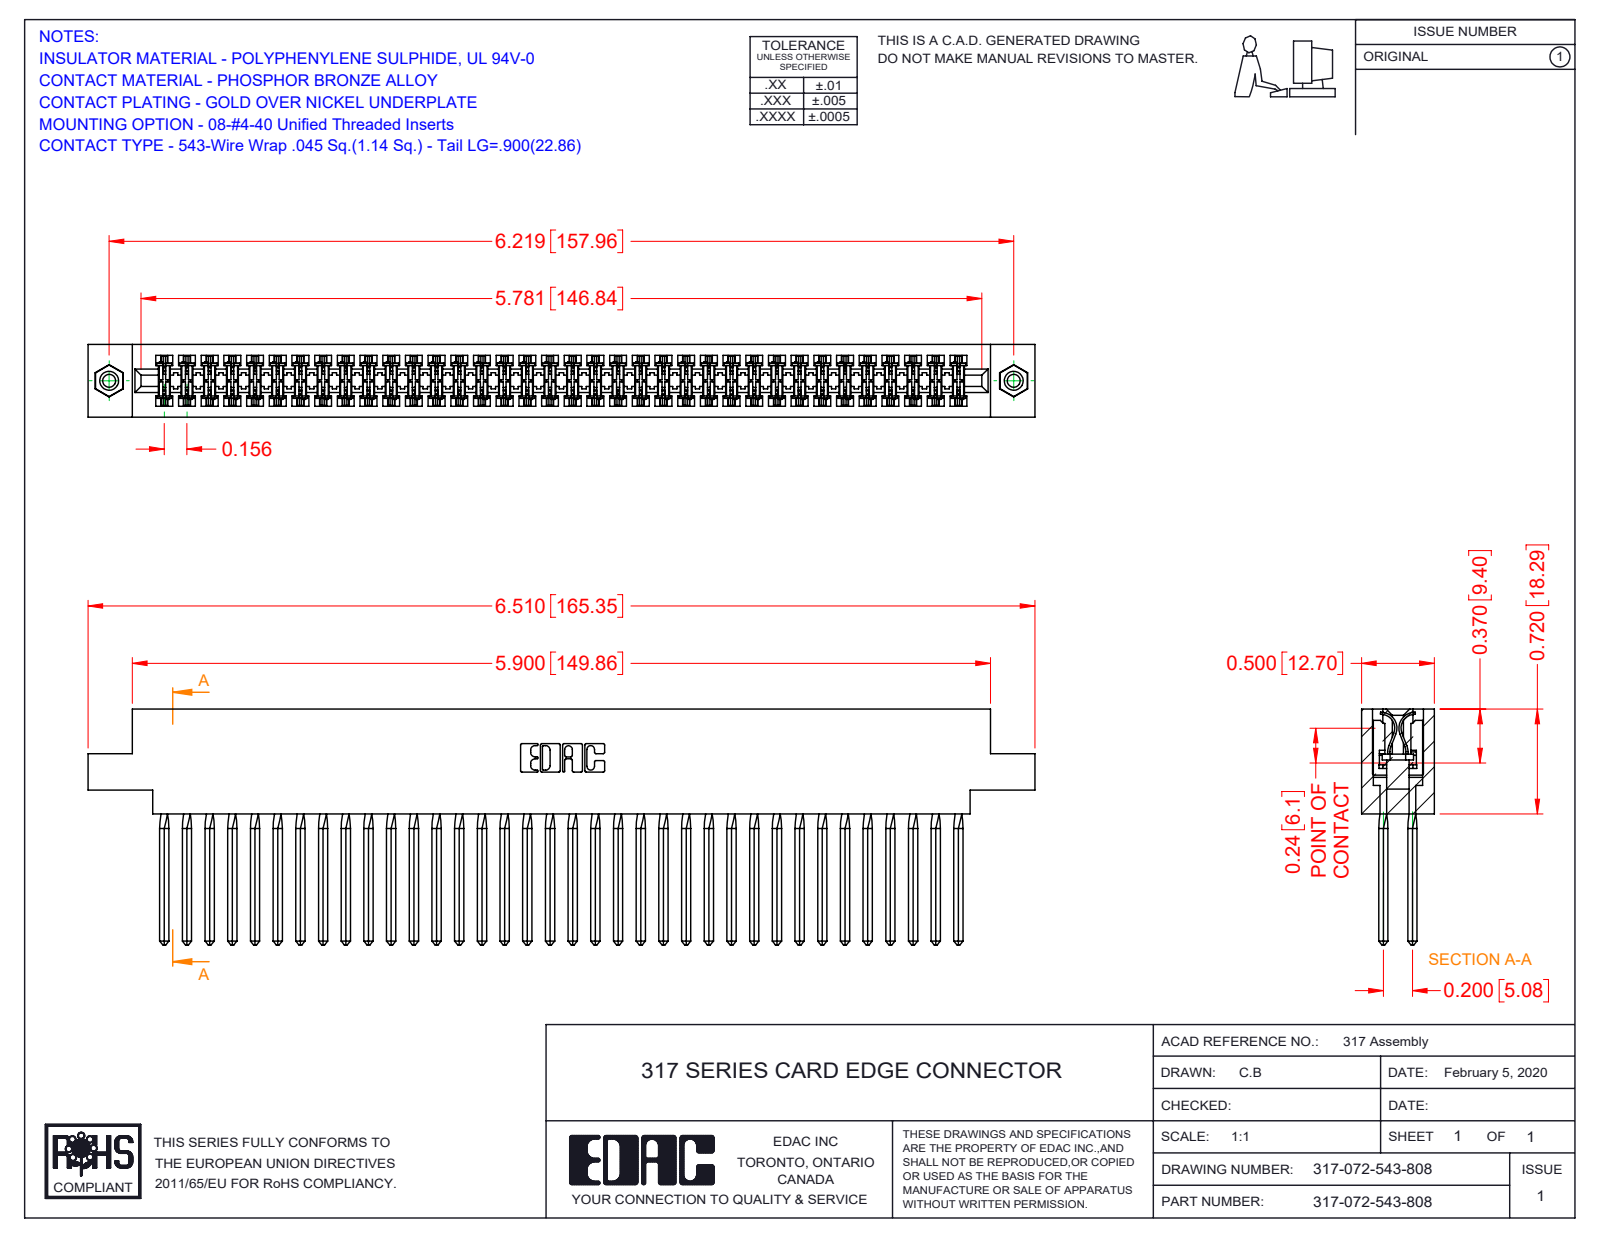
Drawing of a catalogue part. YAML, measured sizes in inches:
part_name: "317-290-001_543; 317-072-543-808; 345-250-001_345-250-003-102; 317 Part_.156 Dia - TI"
step_written_by: "SolidWorks 2016 (CONFIG_CONTROL_DESIGN)"
units: inches
bodies: {solids: 75, faces: 6570, planar: 5346, cylindrical: 920, other: 304}
overall_size: [6.51, 1.62, 0.5]
volume: 1.703
surface_area: 65.27
round_holes:
  - {diameter: 0.089, count: 2}
  - {diameter: 0.125, count: 2}
  - {diameter: 0.156, count: 2}
round_bosses_or_shafts:
  - {diameter: 0.155, count: 2}
partial_cylinders:
  - {radius: 0.015, count: 144}
  - {radius: 0.01, count: 22}
  - {radius: 0.007, count: 6}
  - {radius: 0.031, count: 6}
  - {radius: 0.026, count: 3}
  - {radius: 0.095, count: 2}
  - {radius: 0.1, count: 2}
  - {radius: 0.11, count: 2}
face_to_face_distances: [0.5, 0.075, 0.425, 0.35, 0.11, 0.195, 0.094, 0.2, 0.115, 0.131]
hole_center_spacings: [6.219]
